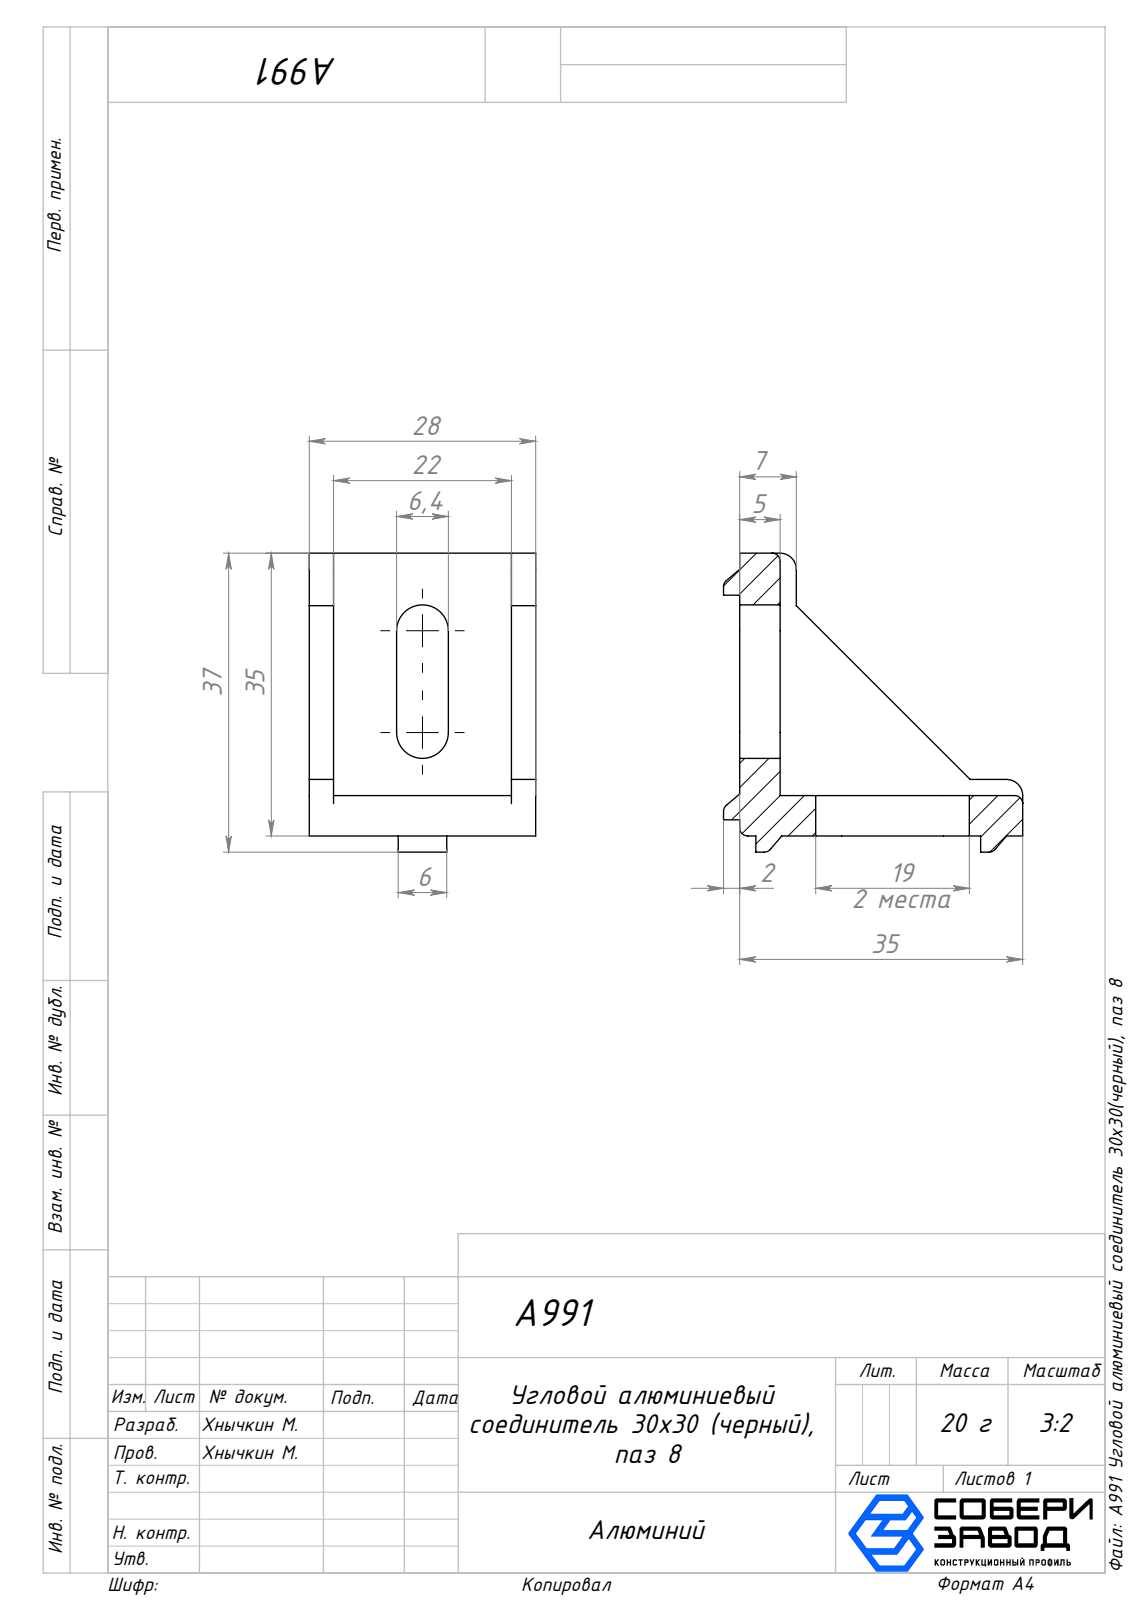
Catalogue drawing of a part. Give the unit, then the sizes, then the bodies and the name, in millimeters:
Units: millimetres
Overall size (bounding box): 37 × 37 × 28
Partial cylindrical surfaces — rounded edges, fillets, slot ends (radius × count): R1 ×7, R3.2 ×4, R2 ×2
Main face-to-face distances: 5, 28, 3, 25, 22, 10.8, 17.2, 7.8, 14.2, 30
Volume: 10 141 mm³ · Surface area: 5 943 mm²
Bodies: 1 solid, 56 faces (40 planar, 16 cylindrical, 0 other)
Part name (STEP PRODUCT): A990 Угловой алюминиевый соединитель 30х30, паз 8
STEP written by: SolidWorks 2025 (AUTOMOTIVE_DESIGN)
